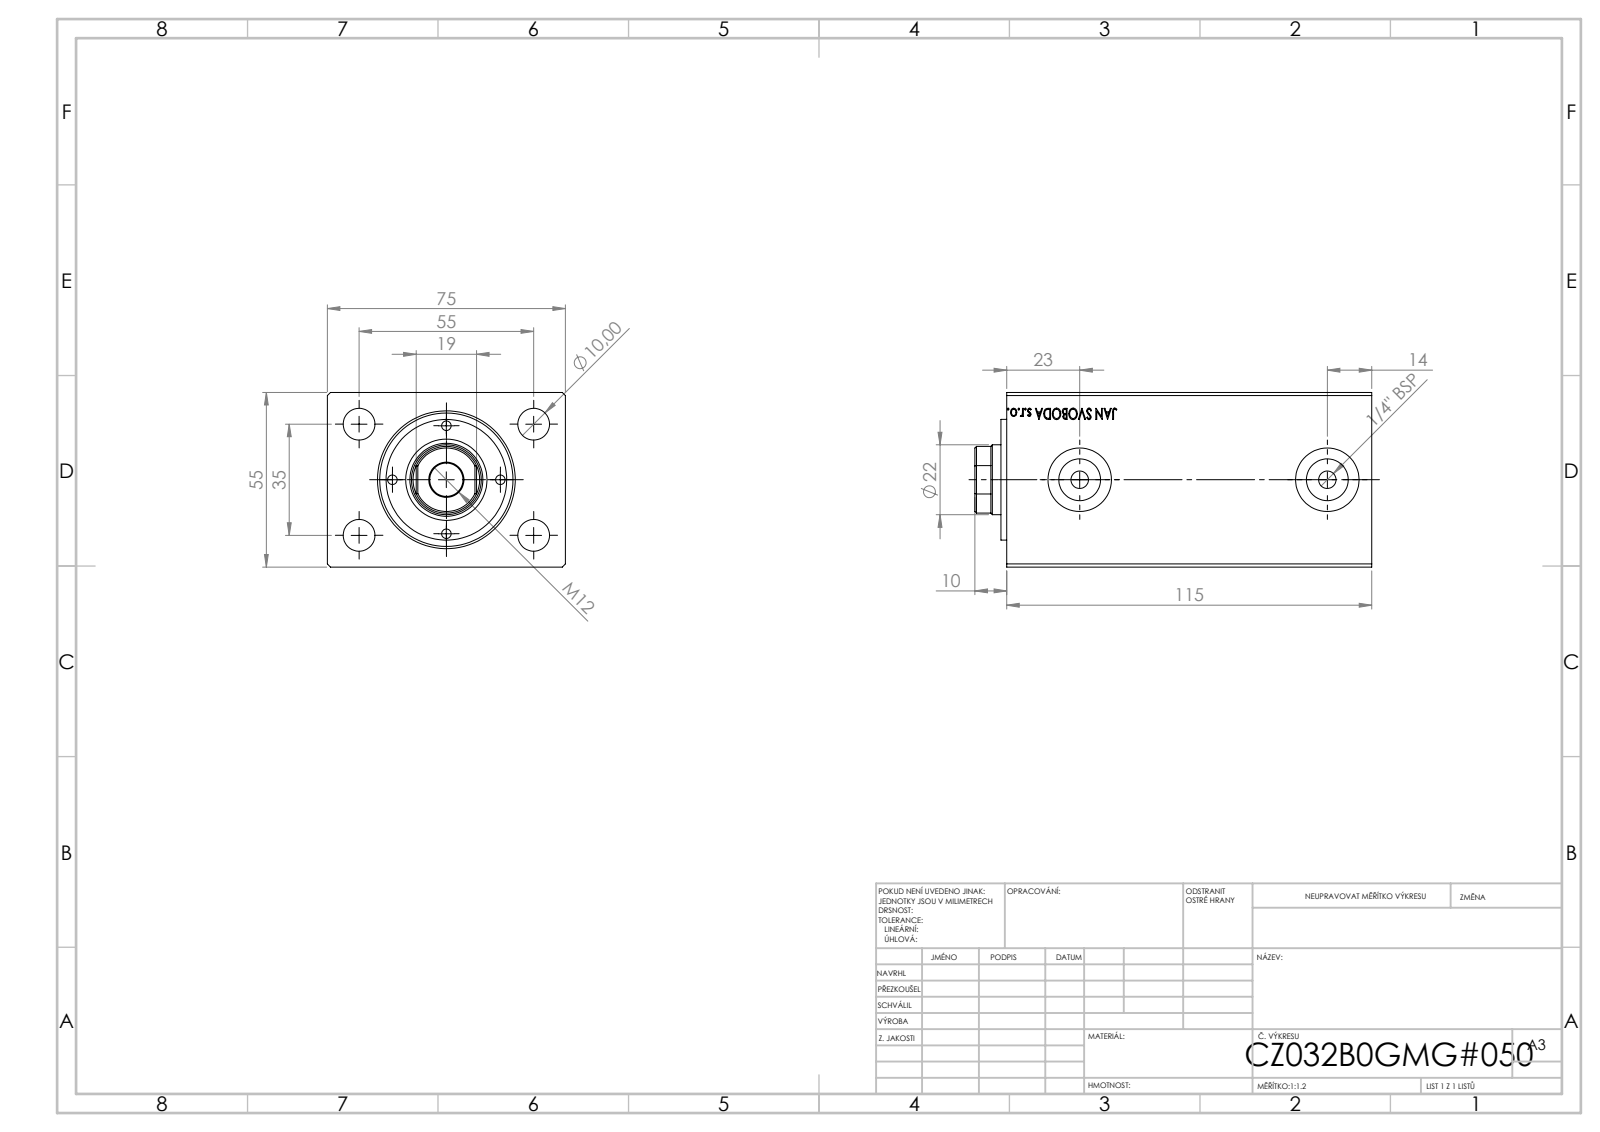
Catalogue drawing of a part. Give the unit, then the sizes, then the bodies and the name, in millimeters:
Units: millimetres
Overall size (bounding box): 125 × 75 × 55
Round holes (diameter × count): ⌀3 ×4, ⌀10 ×4, ⌀5.5 ×2, ⌀13.16 ×2, ⌀20 ×2, ⌀10.5 ×1, ⌀22 ×1, ⌀23 ×1, ⌀32 ×1, ⌀36 ×1, ⌀42 ×1
Round bosses / shafts (diameter × count): ⌀38 ×1
Partial cylindrical surfaces — rounded edges, fillets, slot ends (radius × count): R10.5 ×1
Main face-to-face distances: 55, 75, 115, 101.5, 13.5, 50, 65, 36.5, 49.8, 114.8
Hole centre spacings: 17, 20.41, 24.04, 27.5, 32.6, 44.12, 47.82, 34
Volume: 452 767 mm³ · Surface area: 83 800 mm²
Bodies: 3 solids, 873 faces (399 planar, 58 cylindrical, 416 other)
Part name (STEP PRODUCT): V500CZ; V500CZ_B_VC
STEP written by: SolidWorks 2019 (CONFIG_CONTROL_DESIGN)
